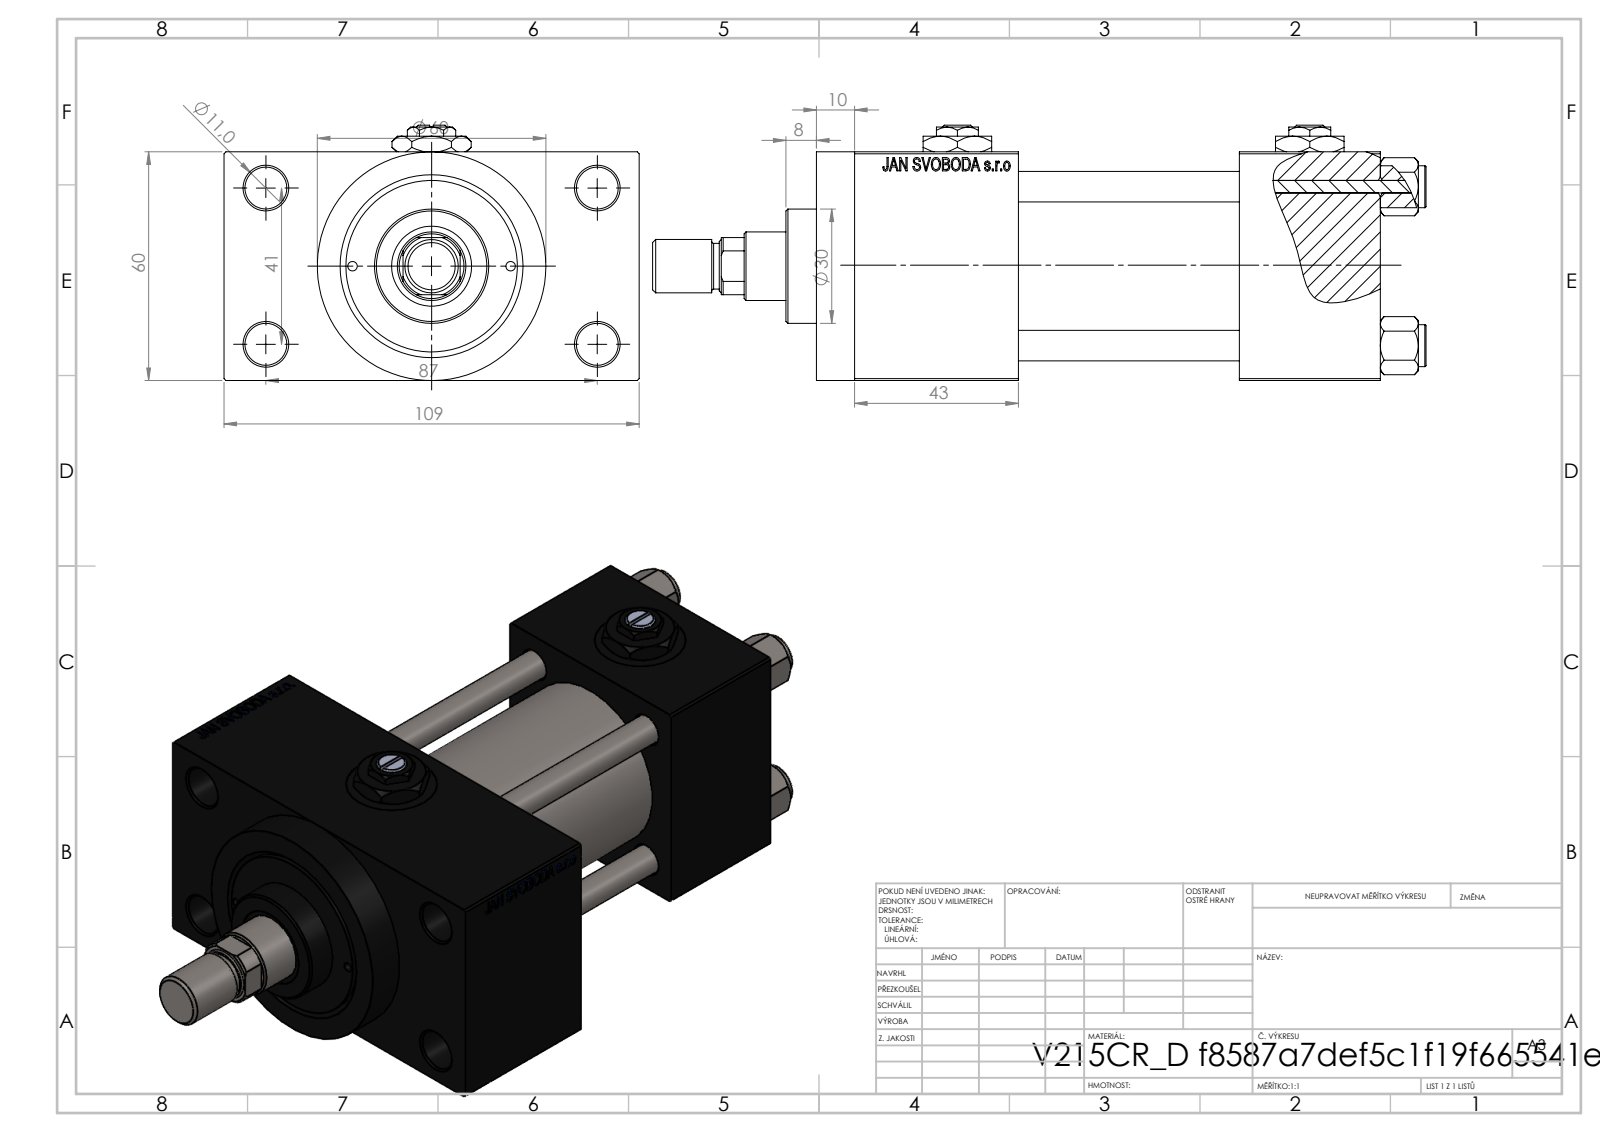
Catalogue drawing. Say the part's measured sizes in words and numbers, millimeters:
The part is named "V215CR_VCP_D; V215_VC_A; NUT_M5_D; ROD_END_AH (+3 more)". Its 3-D file was written by "SolidWorks 2019 (CONFIG_CONTROL_DESIGN)". It is 14 solids with 1227 faces: 552 planar, 107 cylindrical and 568 other. Overall it measures 203 by 109 by 67 millimeters. Its volume is 512 798 cubic millimeters and its surface area 126 275 square millimeters. Round holes: 4 of diameter 8, 4 of diameter 11, 4 of diameter 16.66, 4 of diameter 24, 3 of diameter 7, 2 of diameter 2.5, 1 of diameter 8.5, 1 of diameter 18, 1 of diameter 21, 1 of diameter 31, 1 of diameter 40, 1 of diameter 45. Round bosses or shafts: 4 of diameter 11, 1 of diameter 60, 1 of diameter 46, 1 of diameter 30, 1 of diameter 14, 1 of diameter 12. Partial cylindrical surfaces (rounded edges, fillets, slot ends): 1 of radius 8.5. The main face-to-face distances are 60, 58, 24.5, 84.5, 37, 95, 43, 138, 101, 53. The hole center spacings are 20.85, 22.65, 29.49, 30.62, 41.7, 46.53, 47.15, 48.09.
